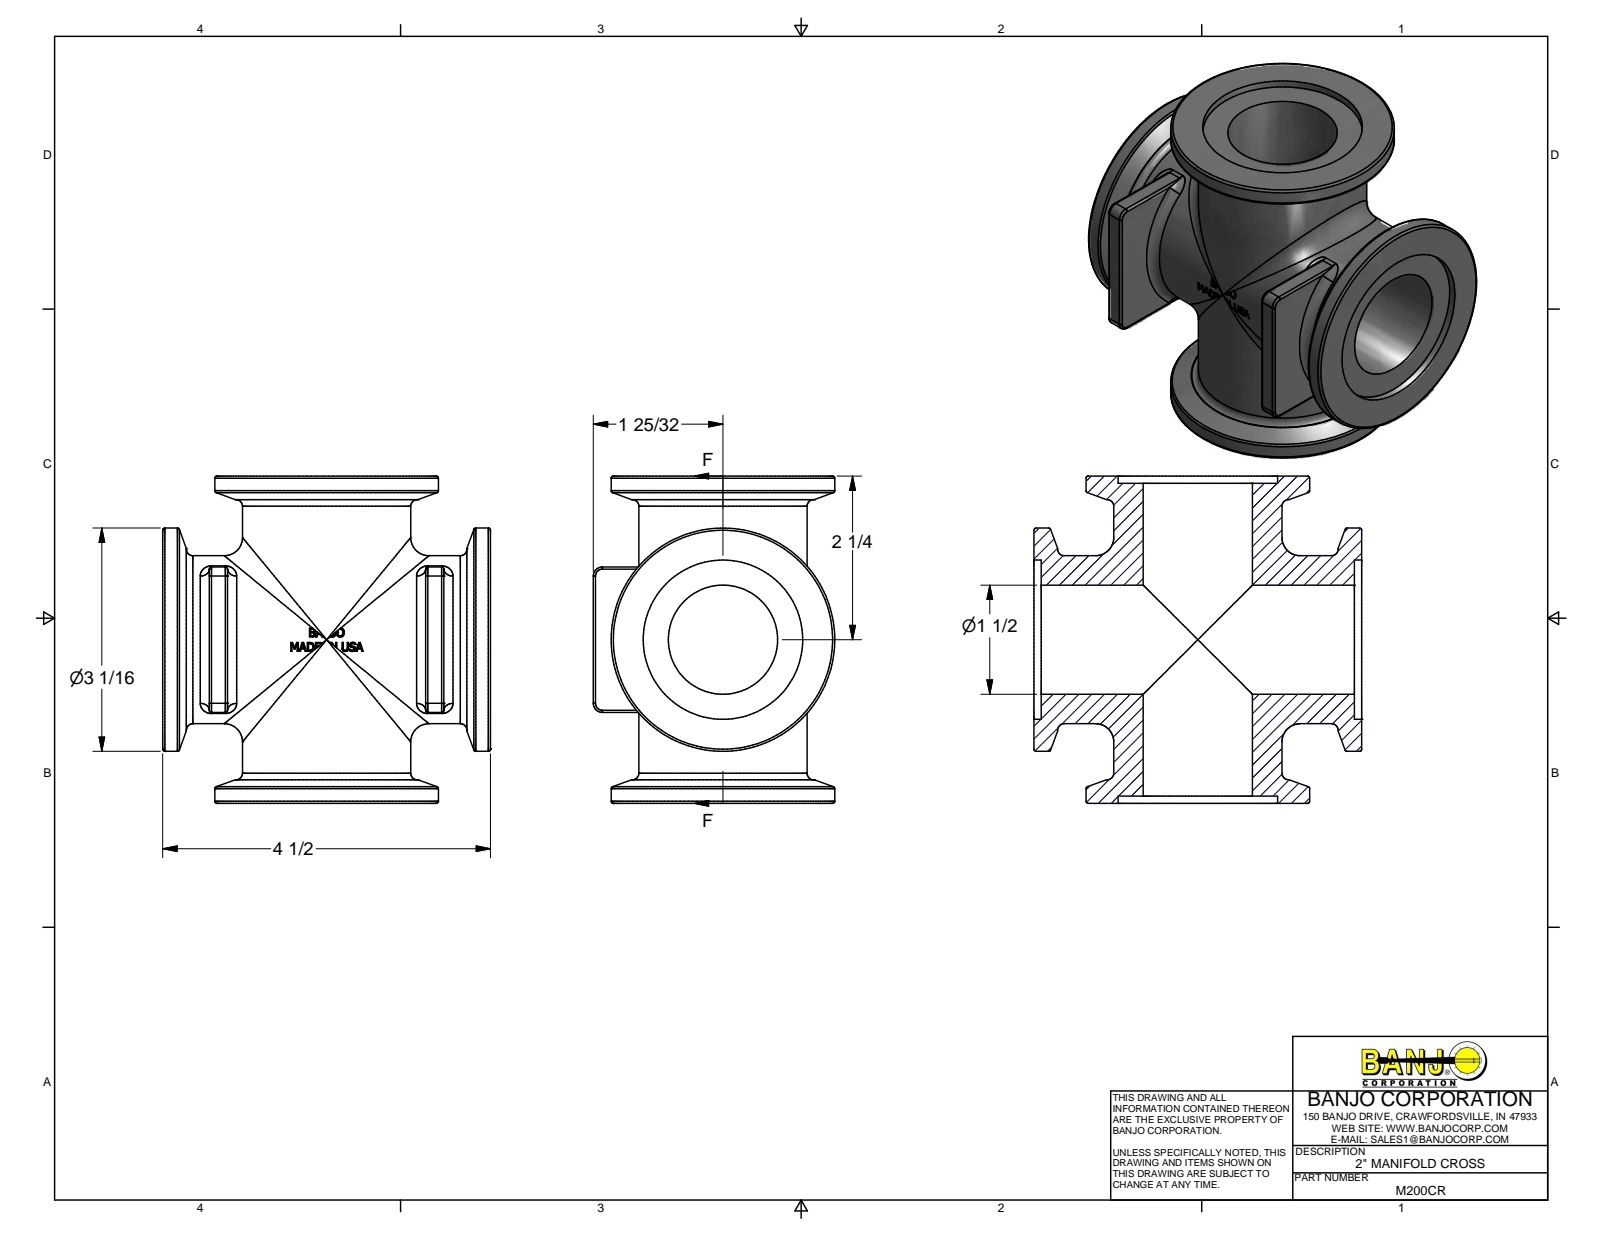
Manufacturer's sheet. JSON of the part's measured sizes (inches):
{"part_name": "M200CR", "step_written_by": "Autodesk Inventor 2013 (AUTOMOTIVE_DESIGN)", "units": "inches", "bodies": {"solids": 1, "faces": 446, "planar": 153, "cylindrical": 90, "other": 203}, "overall_size": [4.5, 4.5, 3.315], "volume_in3": 19.62, "surface_area_in2": 117.9, "round_holes": [[1.5, 2], [2.19, 2]], "round_bosses_or_shafts": [[3.07, 2], [2.31, 2]], "partial_cylinders_radius": [[0.03, 12], [0.125, 4], [1.135, 2]], "face_to_face_distances": [0.1, 4.4, 4.5, 4.3, 0.64, 0.89, 3.61, 3.86, 0.54, 0.79]}
